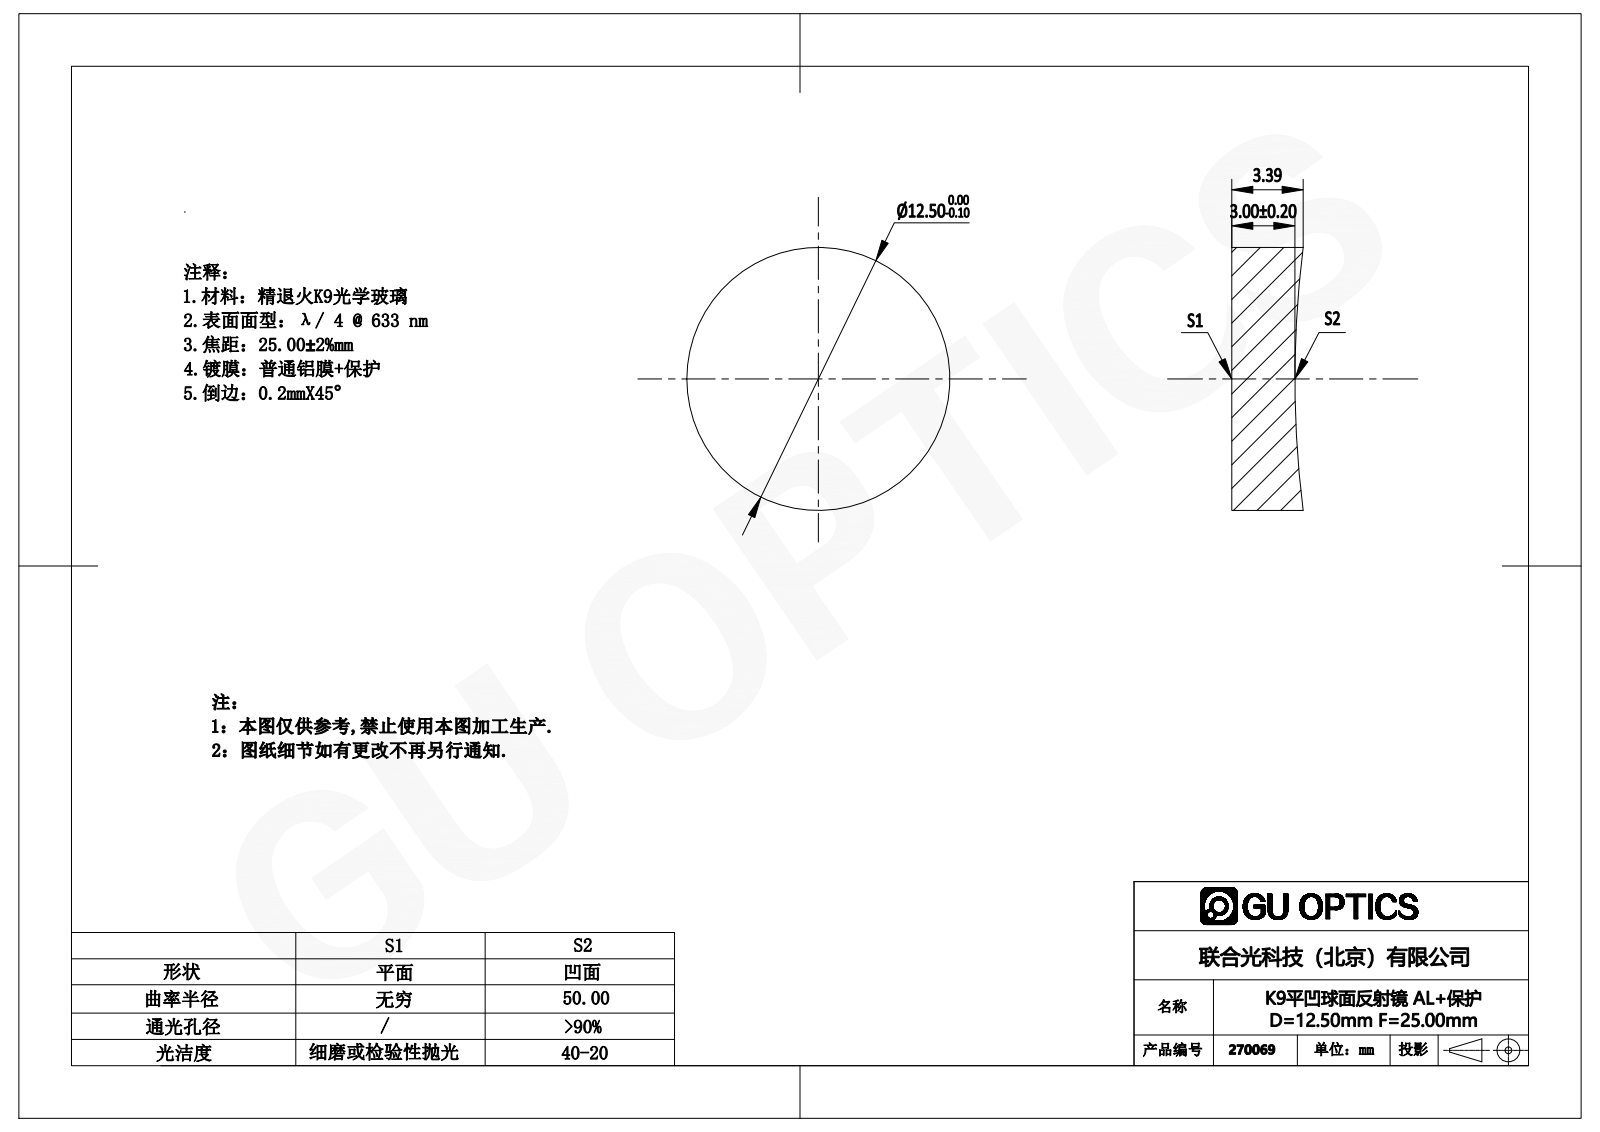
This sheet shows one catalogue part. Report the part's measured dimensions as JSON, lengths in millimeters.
{"part_name": "270004", "step_written_by": "SolidWorks 2016 (AUTOMOTIVE_DESIGN)", "units": "millimeters", "bodies": {"solids": 1, "faces": 5, "planar": 1, "cylindrical": 2, "other": 2}, "overall_size": [12.5, 12.5, 3.39], "volume_mm3": 392, "surface_area_mm2": 379, "round_bosses_or_shafts": [[12.5, 1]]}
